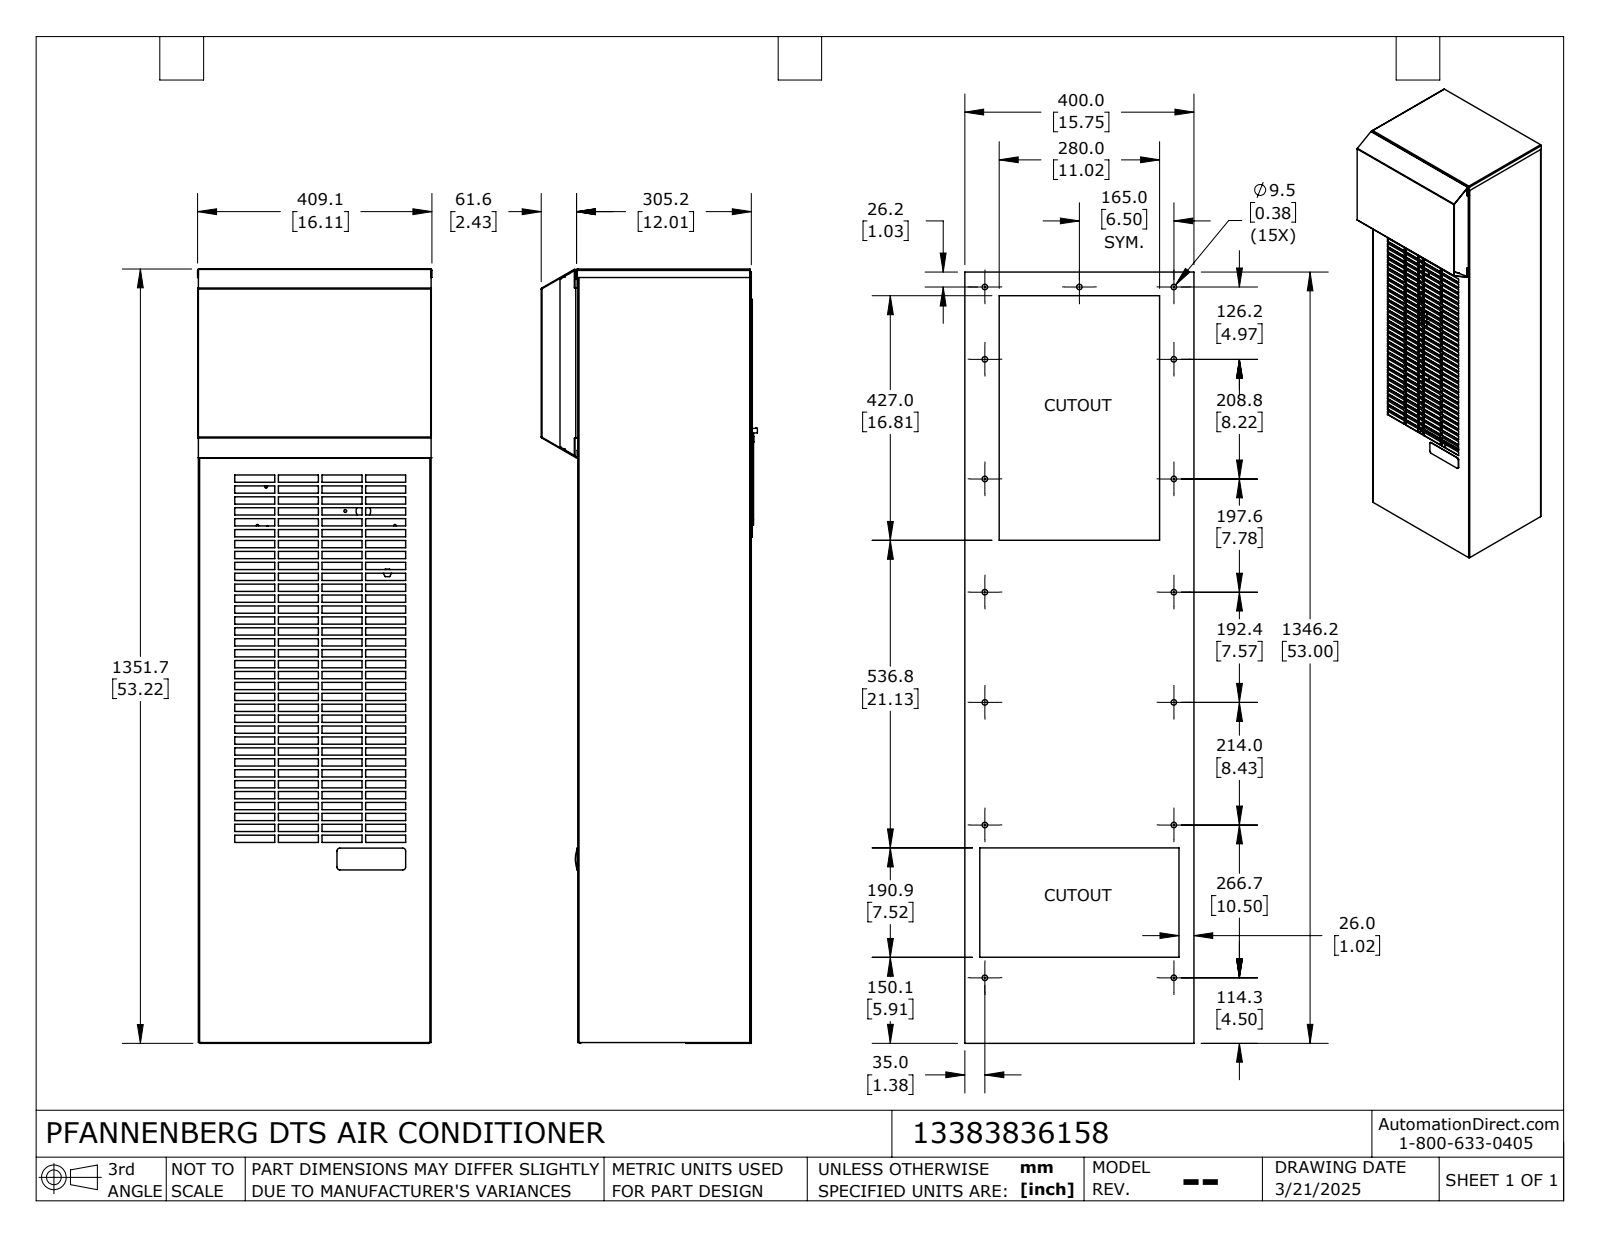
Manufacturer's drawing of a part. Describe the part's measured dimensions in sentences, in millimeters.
The part is named "13383836158_Default". Its 3-D file was written by "SolidWorks 2024 (CONFIG_CONTROL_DESIGN)". It is 25 solids with 3260 faces: 2197 planar, 955 cylindrical and 108 other. Overall it measures 1351.7 by 409.1 by 377.5 millimeters. Its volume is 7 781 000 cubic millimeters and its surface area 7 561 000 square millimeters. Round holes: 72 of diameter 4.2, 18 of diameter 4.2, 15 of diameter 4, 15 of diameter 9.5, 10 of diameter 4.2, 8 of diameter 5, 8 of diameter 6.4, 7 of diameter 6, 5 of diameter 3.3, 4 of diameter 4.5, 4 of diameter 5.5, 2 of diameter 0.6. Round bosses or shafts: 5 of diameter 2, 2 of diameter 7, 2 of diameter 0.8, 1 of diameter 225, 1 of diameter 223, 1 of diameter 149, 1 of diameter 92, 1 of diameter 27. Partial cylindrical surfaces (rounded edges, fillets, slot ends): 140 of radius 3.2, 23 of radius 0.8, 19 of radius 2, 12 of radius 0.8, 12 of radius 2, 9 of radius 0.8, 9 of radius 2, 8 of radius 5. The main face-to-face distances are 1.2, 1.2, 404.9, 4.2, 406.1, 403.7, 110.8, 115, 302.8, 192. The hole center spacings are 0.5, 381, 101.6, 105, 29, 148.5, 203.2, 222.3.
